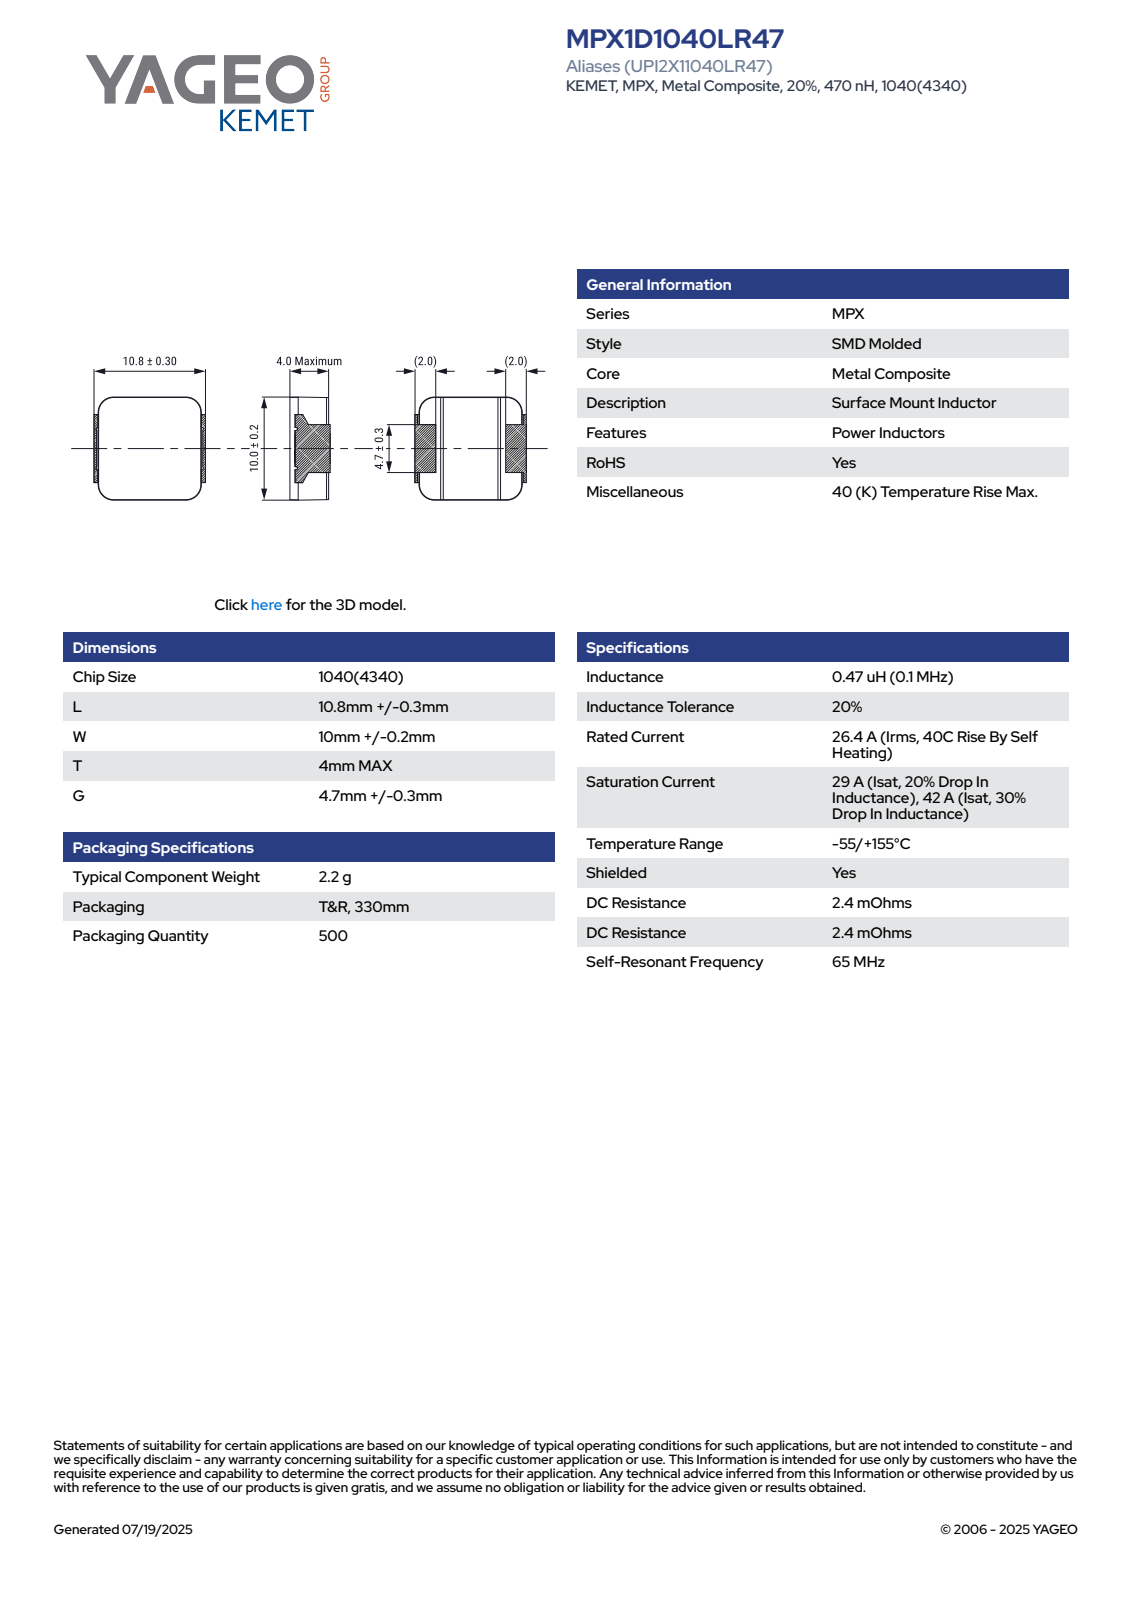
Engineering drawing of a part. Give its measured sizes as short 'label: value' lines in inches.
name: MPX1D1040(4_7)(KEMET)
written by: SolidWorks 2018 (AUTOMOTIVE_DESIGN)
unit: in
bodies: 1 solid, 131 faces (112 planar, 19 cylindrical, 0 other)
size: 0.437 × 0.402 × 0.16
volume: 0.025 in³; area: 0.674 in²
rounds: 4× R0.01, 4× R0.057, 4× R0.059, 3× R0.006
face distances: 0.157, 0.427, 0.15, 0.16, 0.417, 0.437, 0.079, 0.358, 0.069, 0.348
